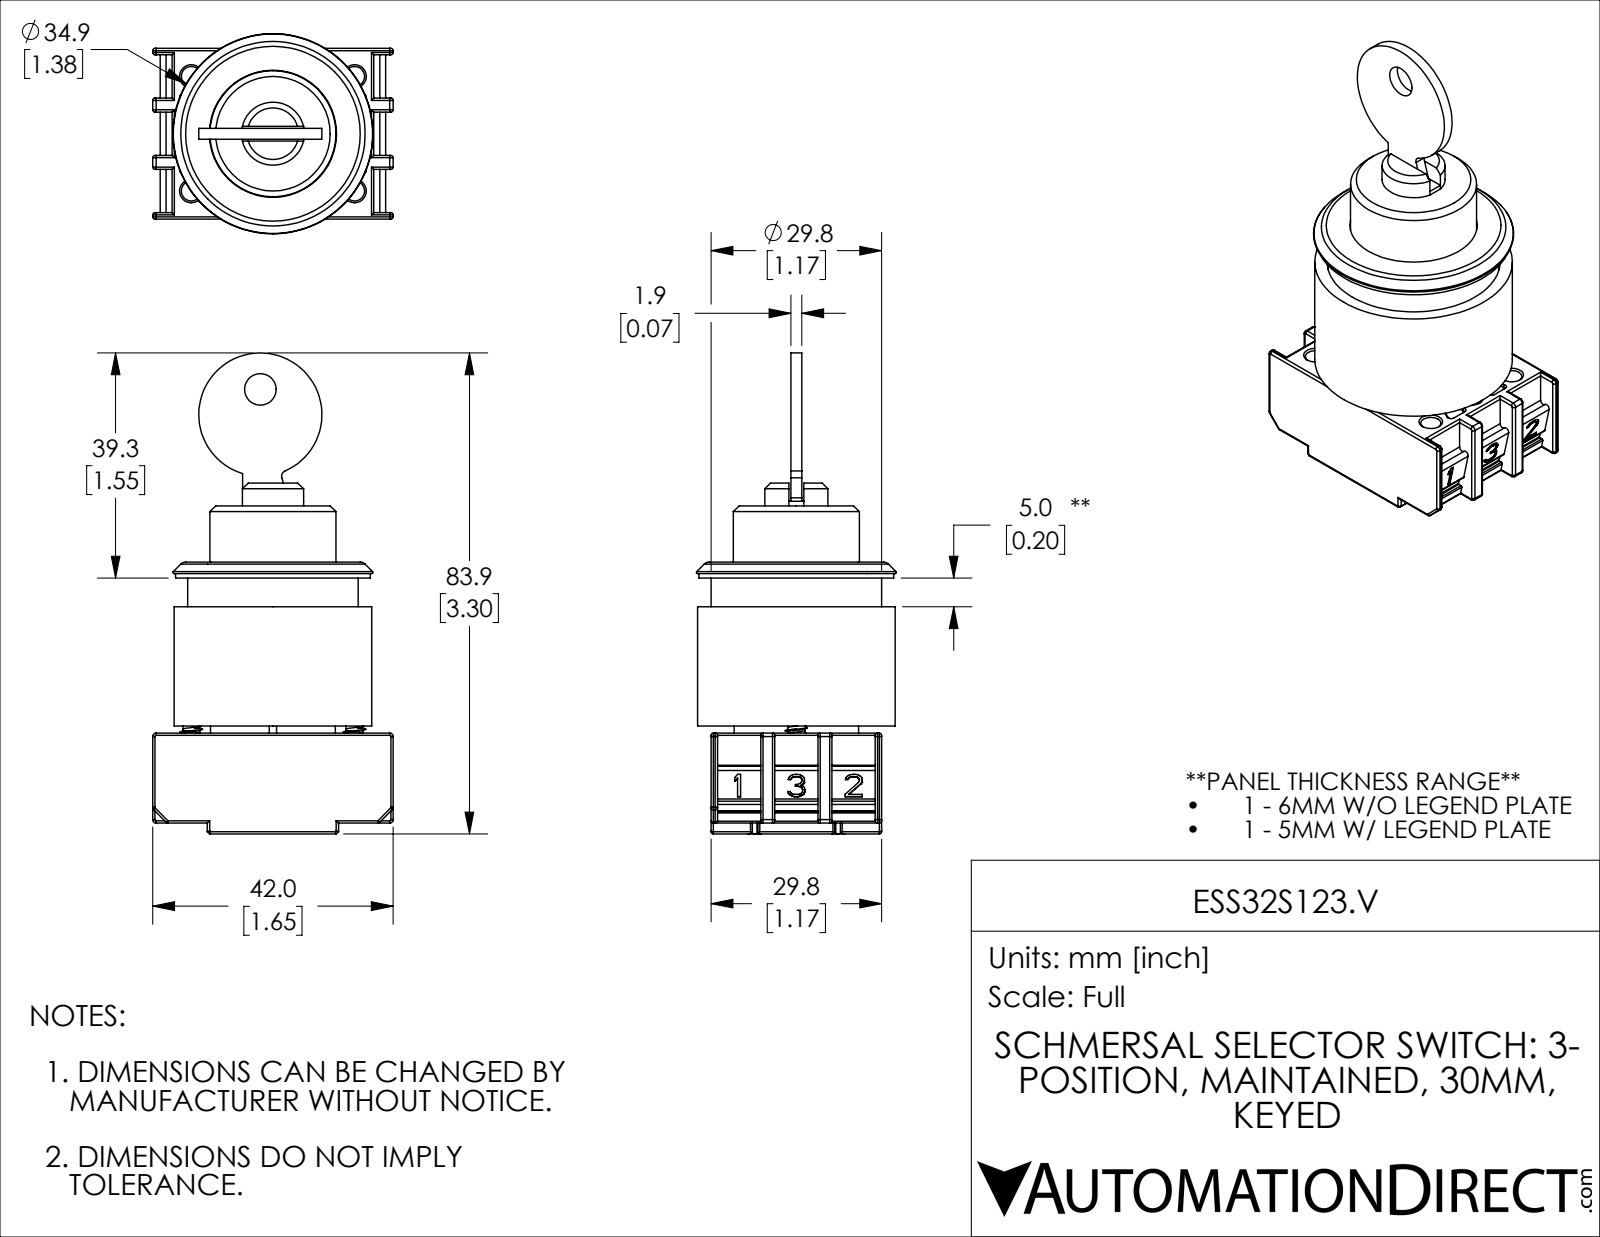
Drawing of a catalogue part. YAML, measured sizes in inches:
part_name: "ESS32S123.V"
step_written_by: "SolidWorks 2019 (CONFIG_CONTROL_DESIGN)"
units: inches
bodies: {solids: 6, faces: 1565, planar: 586, cylindrical: 551, other: 428}
overall_size: [3.305, 1.654, 1.375]
volume: 2.247
surface_area: 42.71
round_holes:
  - {diameter: 0.138, count: 10}
  - {diameter: 0.203, count: 6}
  - {diameter: 0.197, count: 4}
  - {diameter: 0.079, count: 3}
  - {diameter: 0.098, count: 2}
  - {diameter: 0.11, count: 2}
  - {diameter: 0.118, count: 1}
  - {diameter: 0.217, count: 1}
  - {diameter: 0.476, count: 1}
  - {diameter: 0.492, count: 1}
  - {diameter: 0.551, count: 1}
  - {diameter: 0.748, count: 1}
round_bosses_or_shafts:
  - {diameter: 0.189, count: 2}
  - {diameter: 0.115, count: 2}
  - {diameter: 1.358, count: 1}
  - {diameter: 1.339, count: 1}
  - {diameter: 1.173, count: 1}
  - {diameter: 1.004, count: 1}
  - {diameter: 0.866, count: 1}
  - {diameter: 0.858, count: 1}
partial_cylinders:
  - {radius: 0.016, count: 120}
  - {radius: 0.012, count: 48}
  - {radius: 0.008, count: 28}
  - {radius: 0.024, count: 8}
  - {radius: 0.02, count: 7}
  - {radius: 0.031, count: 6}
  - {radius: 0.004, count: 2}
  - {radius: 0.024, count: 2}
face_to_face_distances: [0.634, 0.549, 0.624, 1.173, 0.075, 0.693, 0.683, 0.742, 1.561, 0.394]
hole_center_spacings: [0.391, 0.167, 0.187, 0.236, 0.342, 0.354, 0.394, 0.399]
